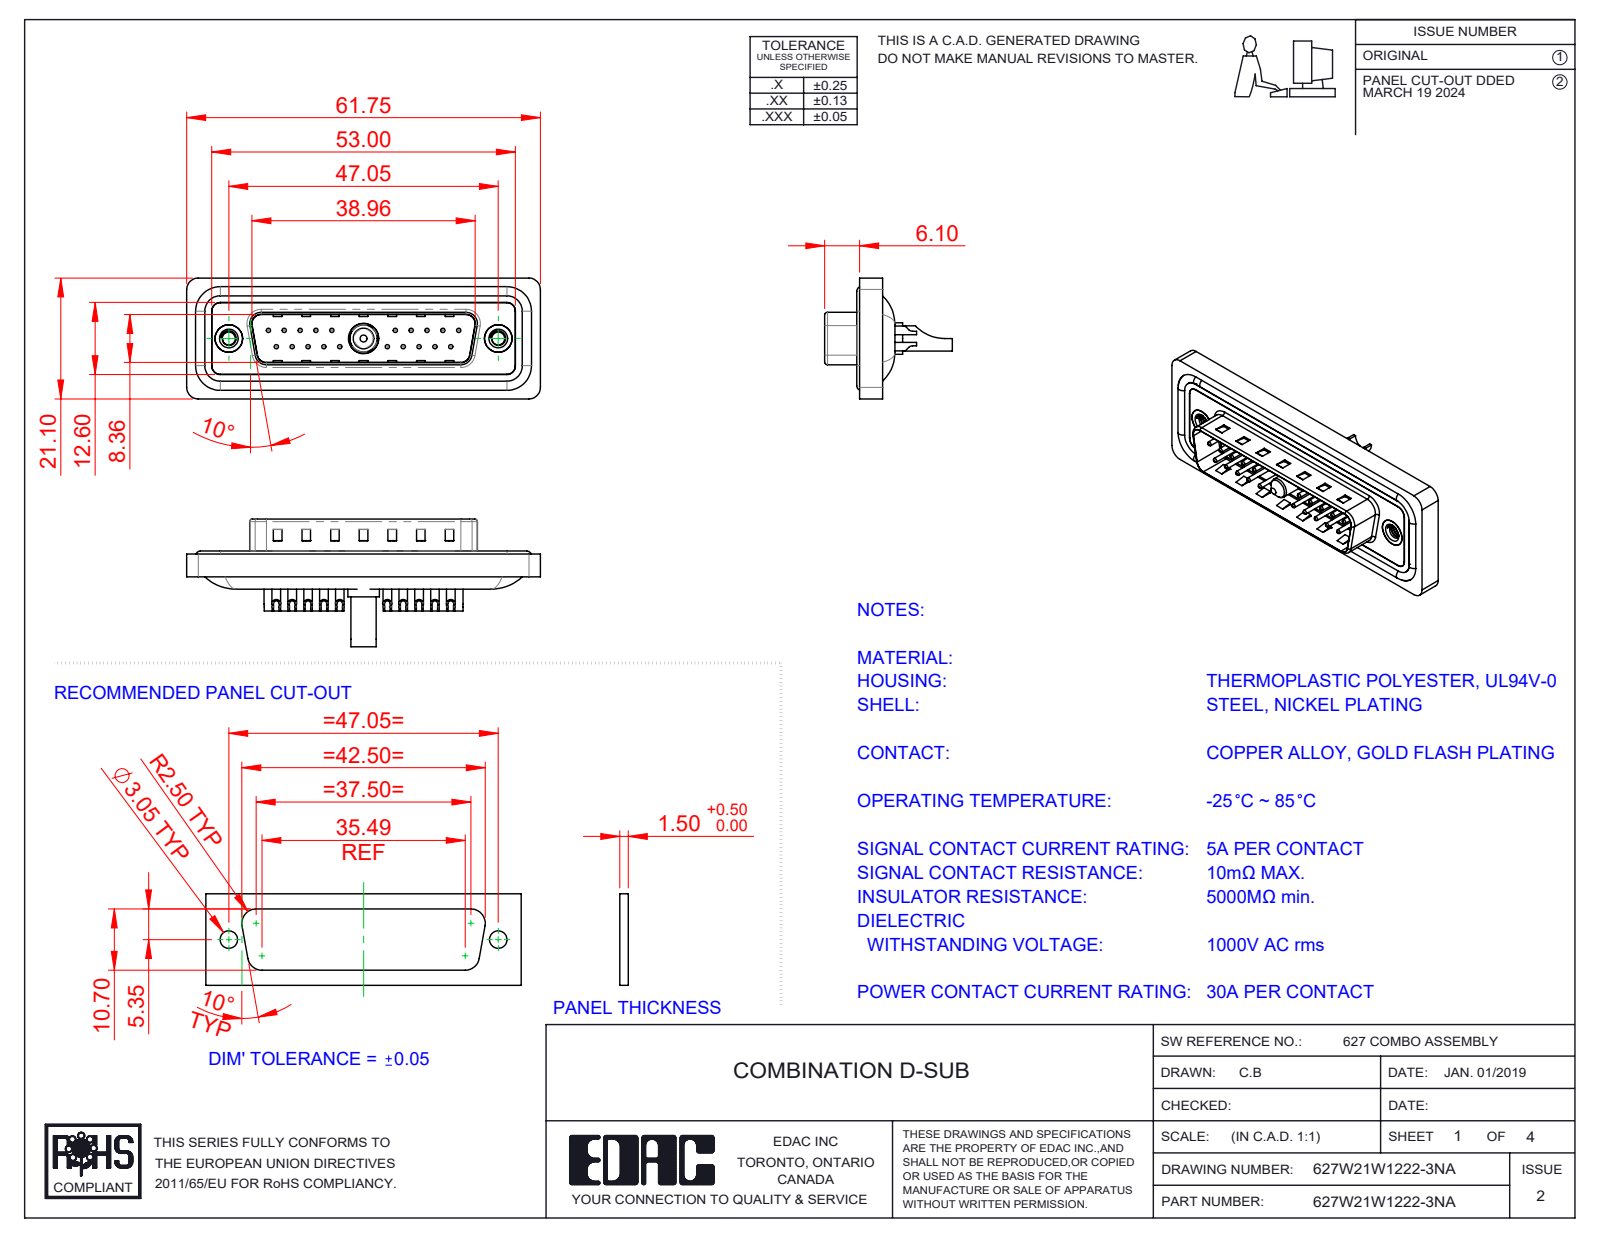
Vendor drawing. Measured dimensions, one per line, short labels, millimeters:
name: 627Combo Threaded Rivet_A; 627Combo Housing_21W1; 627Combo Contact Row 2_22; Power Pin_30A SC (+5 more)
written by: SolidWorks 2023 (CONFIG_CONTROL_DESIGN)
unit: mm
bodies: 29 solids, 1266 faces (402 planar, 532 cylindrical, 332 other)
size: 61.75 × 22.3 × 21.1
volume: 7 254 mm³; area: 12 218 mm²
holes: 20× ⌀0.75, 20× ⌀1, 20× ⌀1.6, 20× ⌀2, 2× ⌀2.26, 2× ⌀4, 2× ⌀4.8, 2× ⌀5, 1× ⌀3.5, 1× ⌀4.85, 1× ⌀5.3
bosses: 20× ⌀1.5, 4× ⌀1.6, 2× ⌀4.9, 1× ⌀5.5, 1× ⌀5.2, 1× ⌀4.75, 1× ⌀4.4, 1× ⌀3.75
rounds: 22× R1.5, 18× R2, 8× R0.5, 8× R1.6, 6× R1, 4× R0.25, 4× R0.6, 4× R0.65
face distances: 0.4, 1.5, 1.1, 1.6, 0.5, 3.1, 2.9, 4.1, 0.82, 9.58
hole spacings: 3.16, 2.77, 5.54, 8.31, 5.04, 19.39, 20.97, 22.16
